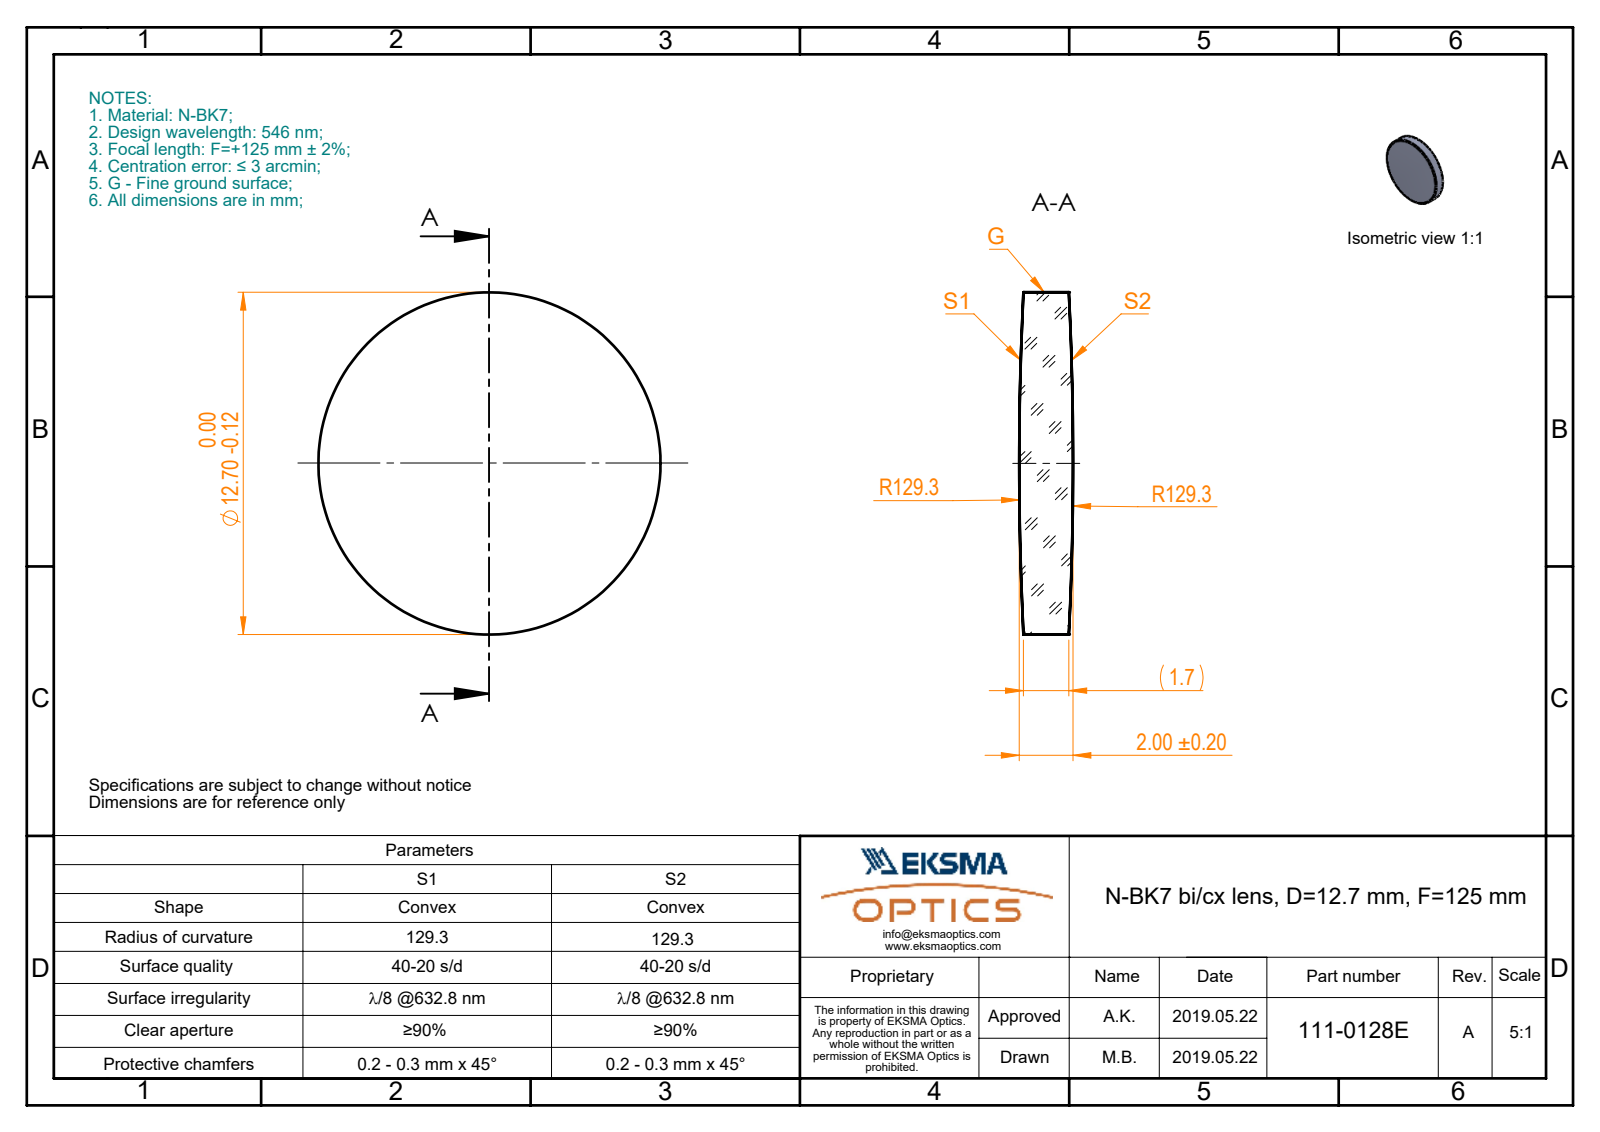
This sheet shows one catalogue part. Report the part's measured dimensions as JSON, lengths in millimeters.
{"part_name": "111-0128E BK7 bi-cx 12.7 F125", "step_written_by": "SolidWorks 2017 (CONFIG_CONTROL_DESIGN)", "units": "millimeters", "bodies": {"solids": 1, "faces": 6, "planar": 0, "cylindrical": 2, "other": 4}, "overall_size": [12.7, 12.7, 2], "volume_mm3": 234, "surface_area_mm2": 321, "round_bosses_or_shafts": [[12.7, 1]]}
